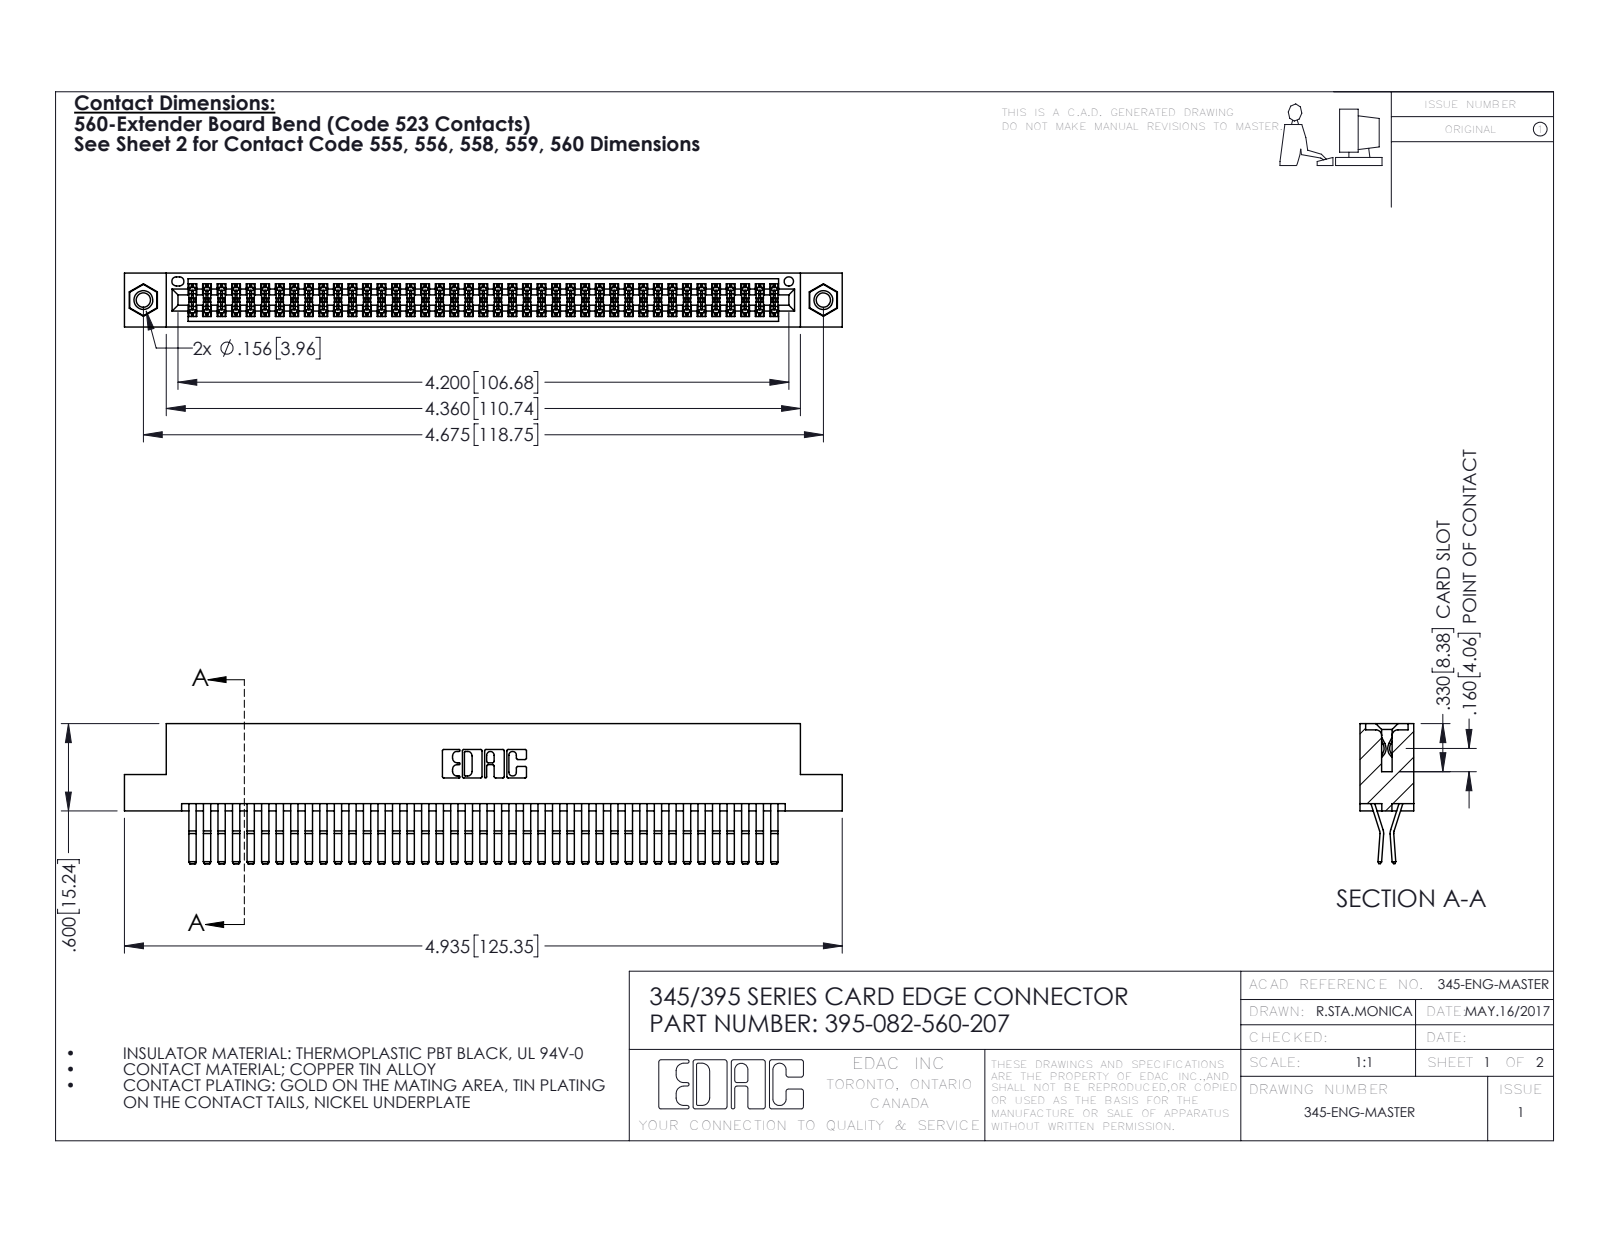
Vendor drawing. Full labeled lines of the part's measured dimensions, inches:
Part name (STEP PRODUCT): 345-250-001_345-250-005-103; 395-082-560-207; 345 Part_Flush Mounting Lugs - 0.156 Dia-TI; 345-292-001_560 Tail
STEP written by: SolidWorks 2016 (CONFIG_CONTROL_DESIGN)
Units: inches
Bodies: 85 solids, 4450 faces (2818 planar, 1616 cylindrical, 16 other)
Overall size (bounding box): 4.935 × 0.962 × 0.37
Volume: 0.774 in³ · Surface area: 31.23 in²
Round holes (diameter × count): ⌀0.098 ×2, ⌀0.125 ×2, ⌀0.156 ×2, ⌀0.064 ×1
Round bosses / shafts (diameter × count): ⌀0.155 ×2
Partial cylindrical surfaces — rounded edges, fillets, slot ends (radius × count): R0.006 ×123, R0.01 ×22, R0.007 ×6, R0.031 ×6, R0.026 ×3, R0.01 ×2, R0.014 ×2, R0.019 ×2
Main face-to-face distances: 0.025, 0.072, 0.298, 0.37, 0.2, 0.098, 0.272, 0.225, 0.175, 0.149
Hole centre spacings: 0.27, 4.439, 4.675
